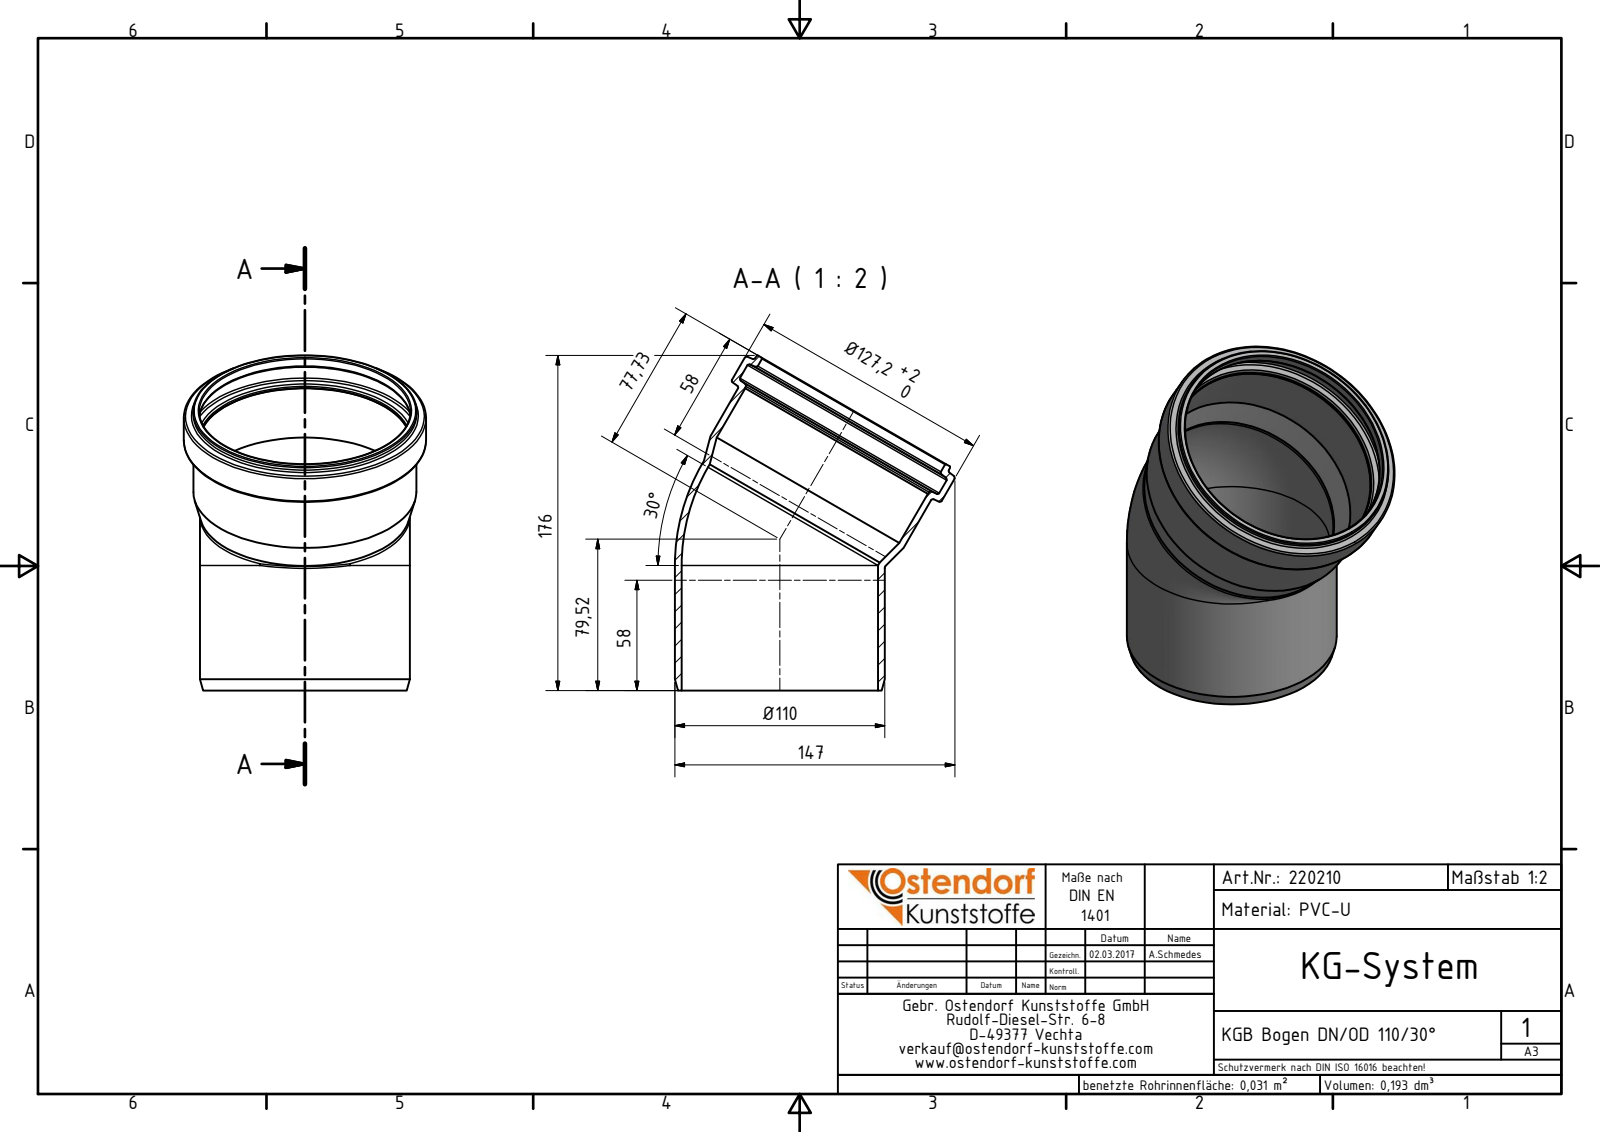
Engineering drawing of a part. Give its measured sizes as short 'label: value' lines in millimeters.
name: 220210 KGB Bogen DN_OD 110_30°
written by: Autodesk Inventor 2016 (AUTOMOTIVE_DESIGN)
unit: mm
bodies: 1 solid, 34 faces (3 planar, 11 cylindrical, 20 other)
size: 176 × 147 × 127.2
volume: 185 621 mm³; area: 116 066 mm²
holes: 2× ⌀103.2, 1× ⌀110.7, 1× ⌀111, 1× ⌀120.8
bosses: 2× ⌀110.2, 1× ⌀127.2, 1× ⌀117.4, 1× ⌀117.1
face distances: 18.26
